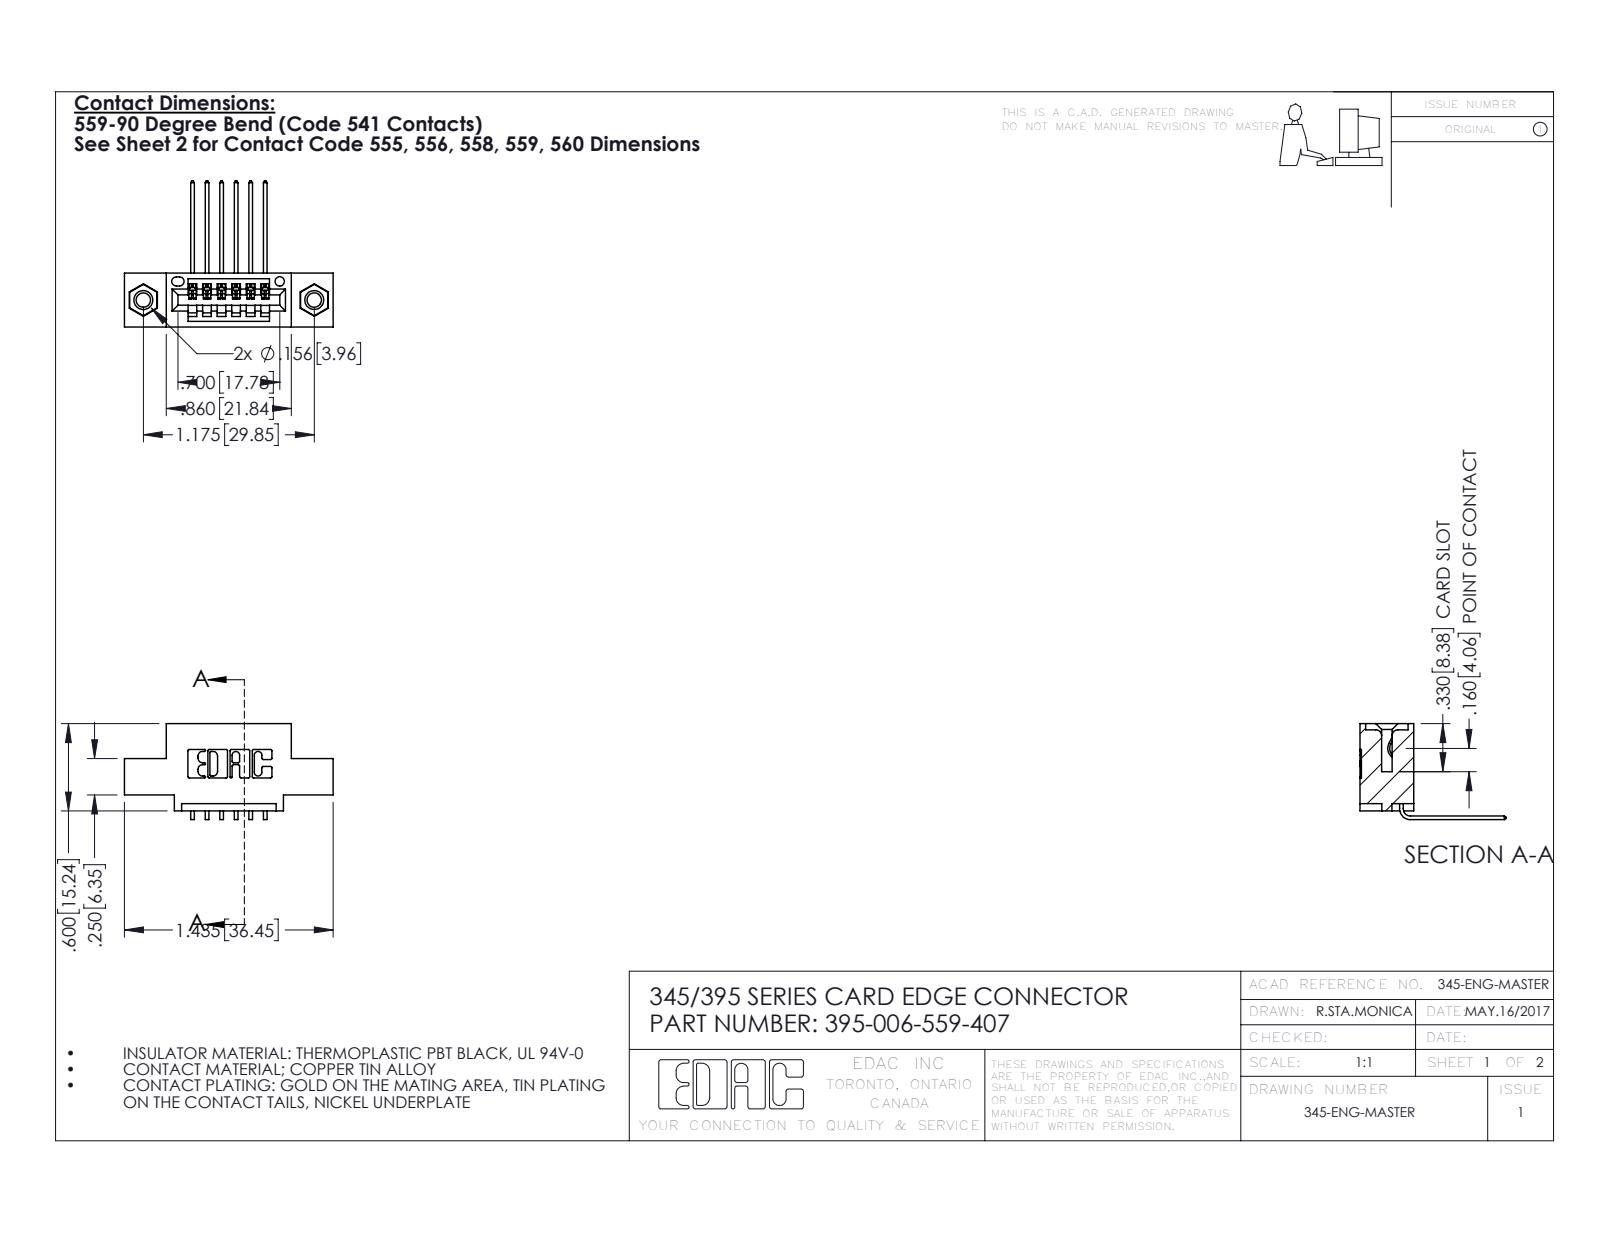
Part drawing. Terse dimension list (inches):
name: 345-250-001_345-250-005-103; 345 Part_0.110 Offset - 0.156 Dia-TI; 345-292-001_558 559 Tail - 1; 395-006-559-407
written by: SolidWorks 2016 (CONFIG_CONTROL_DESIGN)
unit: in
bodies: 9 solids, 550 faces (368 planar, 166 cylindrical, 16 other)
size: 1.435 × 1.005 × 0.659
volume: 0.189 in³; area: 5.987 in²
holes: 2× ⌀0.098, 2× ⌀0.125, 2× ⌀0.156, 1× ⌀0.064
bosses: 2× ⌀0.155
rounds: 22× R0.01, 12× R0.006, 6× R0.007, 6× R0.031, 3× R0.026, 2× R0.031, 2× R0.04, 1× R0.014
face distances: 0.2, 0.37, 0.1, 0.072, 0.298, 0.16, 0.025, 0.06, 0.3, 0.04
hole spacings: 0.27, 0.946, 1.175
